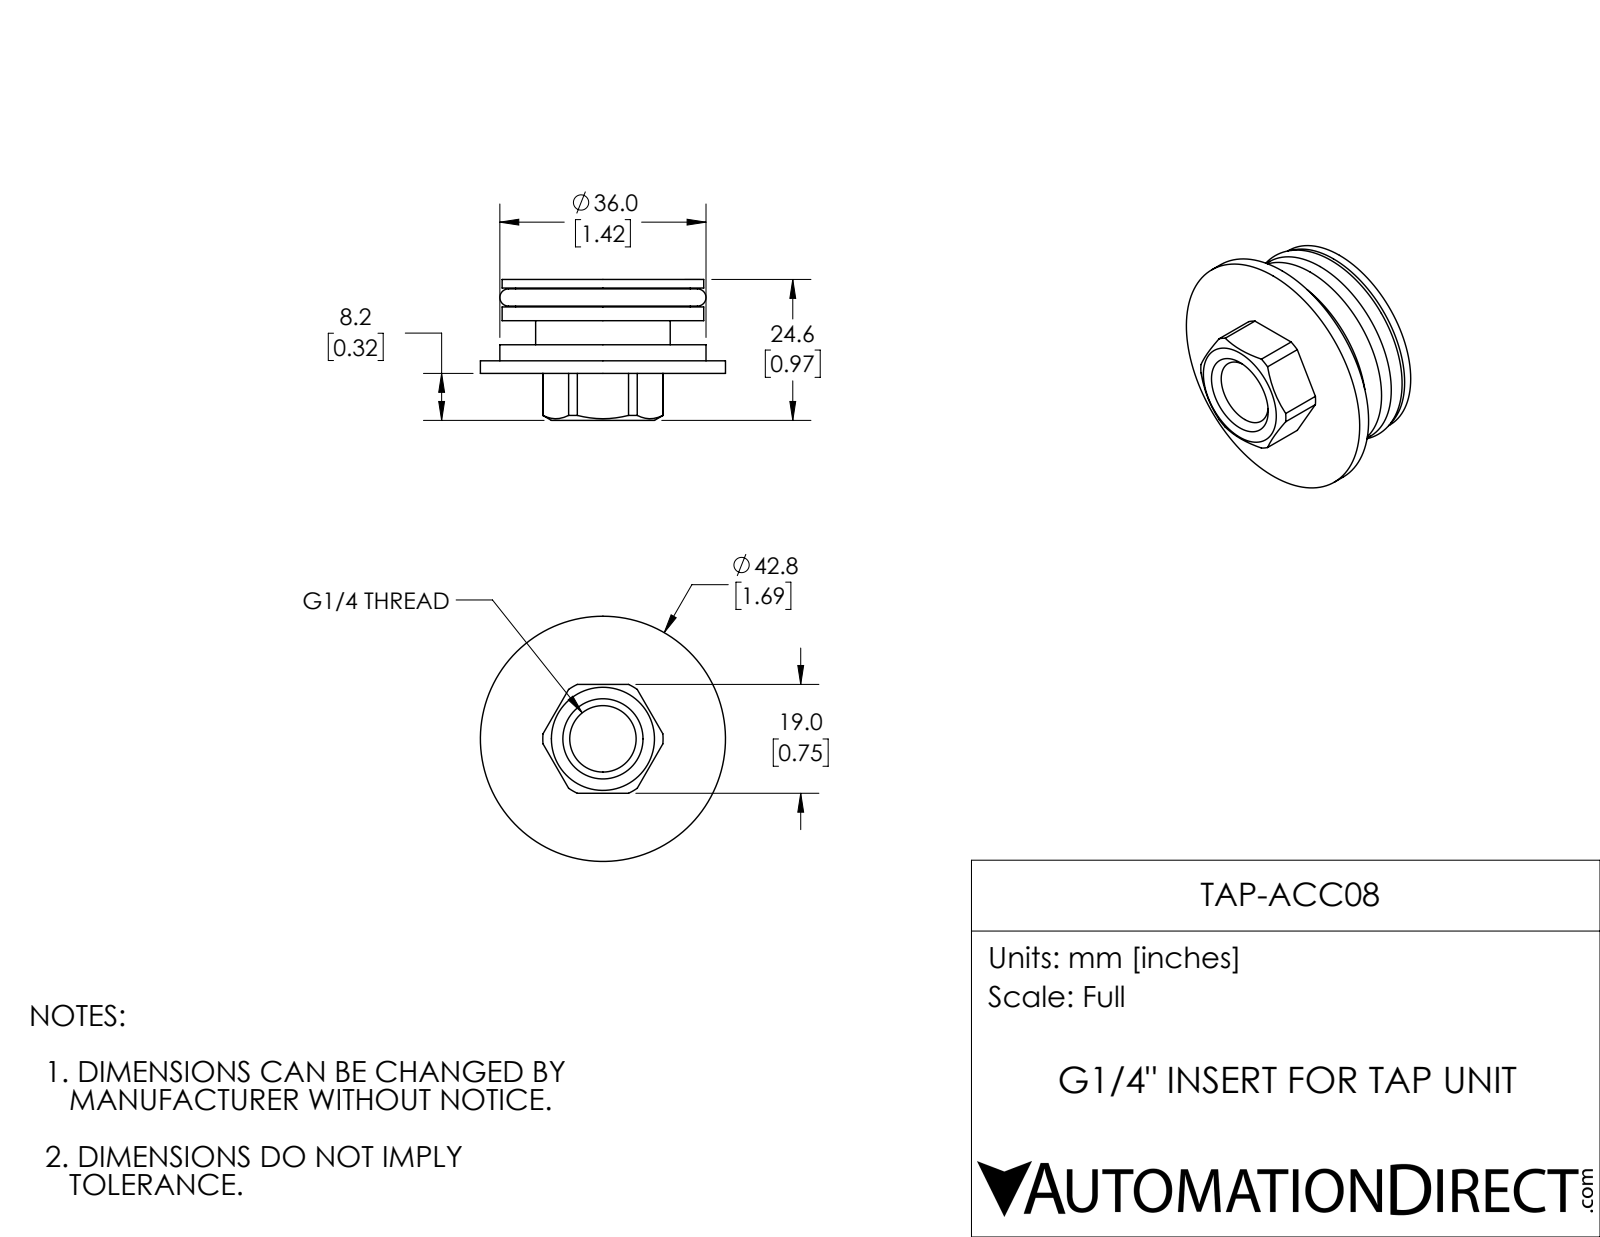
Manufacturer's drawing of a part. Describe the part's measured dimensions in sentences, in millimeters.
The part is named "TAP-ACC08". Its 3-D file was written by "SolidWorks 2017 (AUTOMOTIVE_DESIGN)". It is 1 solid with 48 faces: 14 planar, 24 cylindrical and 10 other. Overall it measures 42.8 by 42.8 by 24.6 millimeters. Its volume is 12 500 cubic millimeters and its surface area 7 929 square millimeters. Round holes: 1 of diameter 11.6, 1 of diameter 26. Round bosses or shafts: 1 of diameter 42.8, 1 of diameter 36, 1 of diameter 35.2, 1 of diameter 30.5, 1 of diameter 23.5. Partial cylindrical surfaces (rounded edges, fillets, slot ends): 1 of radius 10.5. The main face-to-face distances are 5, 9.2, 4.2, 16.4, 11.4, 7.2, 2.2, 2.8, 7, 14.2.
